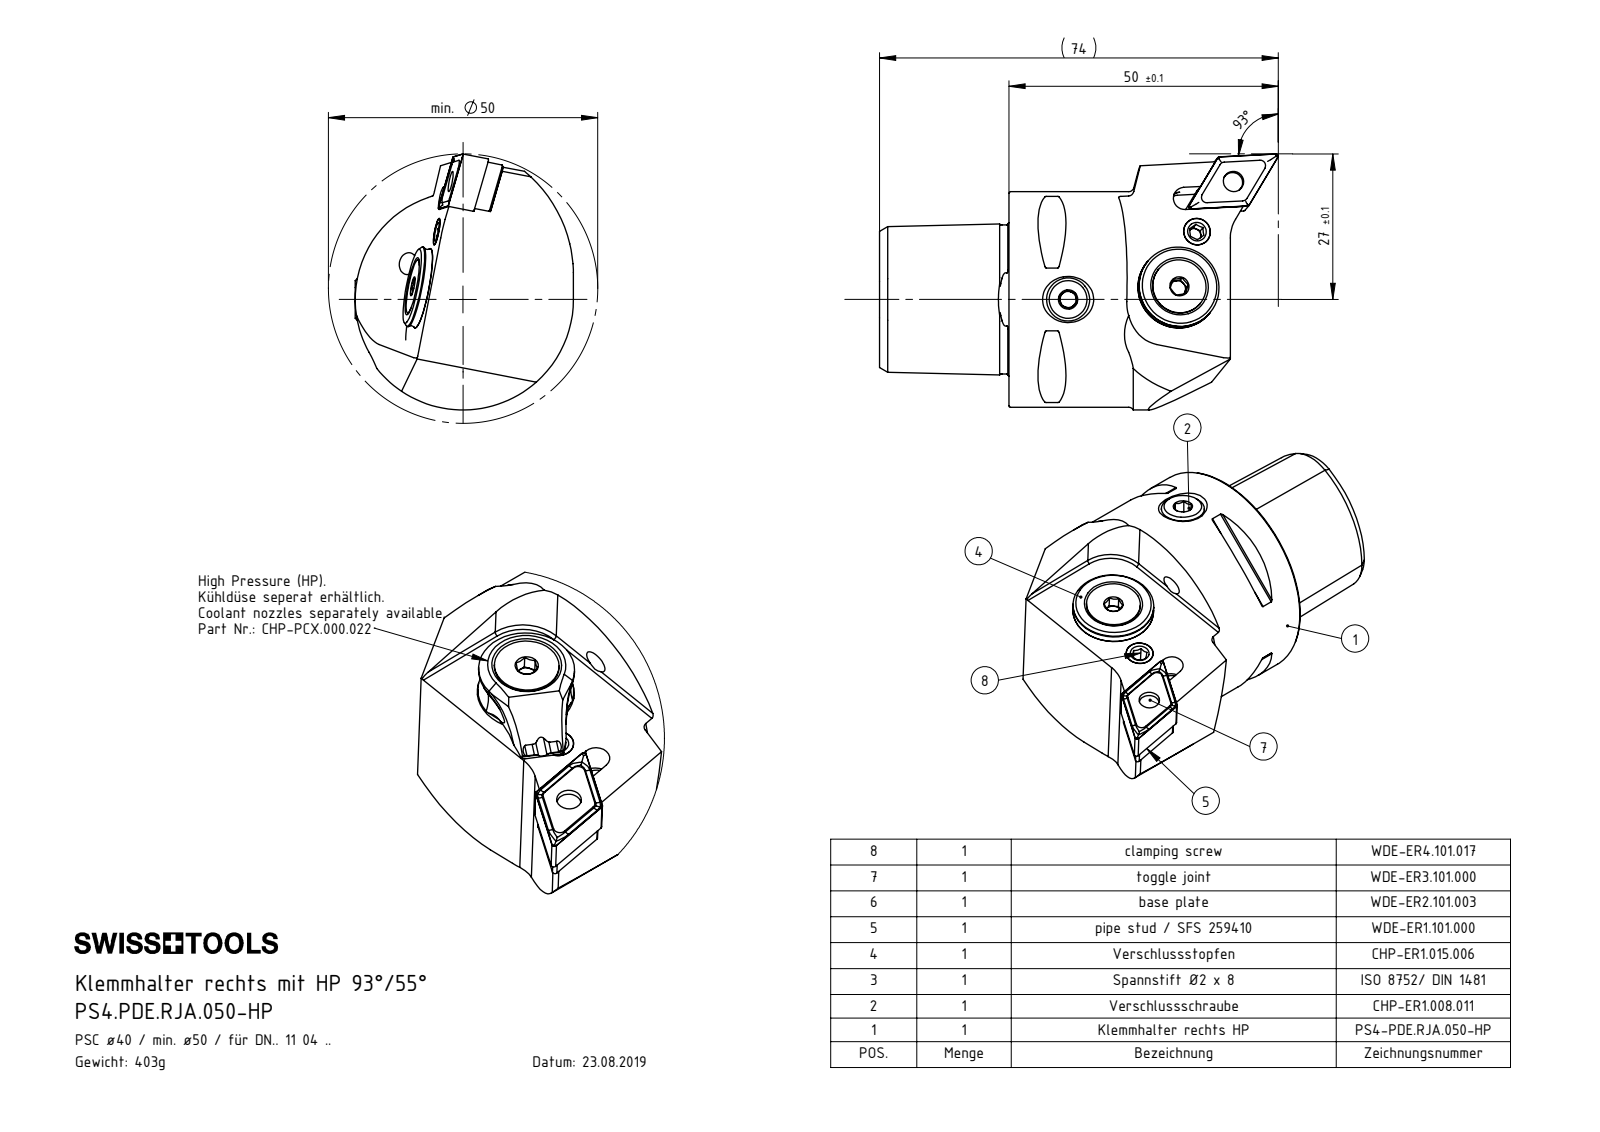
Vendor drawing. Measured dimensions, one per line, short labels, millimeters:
name: DIN 3771 - 6.5x1.5; CHP-ER1.008.011_A; DNMG110404; ISO 8752 2x8 (+8 more)
written by: SolidWorks 2022 (CONFIG_CONTROL_DESIGN)
unit: mm
bodies: 12 solids, 563 faces (159 planar, 143 cylindrical, 261 other)
size: 74 × 47.49 × 40.5
volume: 52 225 mm³; area: 17 398 mm²
holes: 2× ⌀3.3, 2× ⌀5, 1× ⌀1.2, 1× ⌀2, 1× ⌀2.5, 1× ⌀3, 1× ⌀3.81, 1× ⌀4, 1× ⌀4.2, 1× ⌀4.6, 1× ⌀4.8, 1× ⌀5.3
bosses: 1× ⌀40, 1× ⌀14.85, 1× ⌀13.4, 1× ⌀10, 1× ⌀8, 1× ⌀6, 1× ⌀5.9, 1× ⌀5.5
rounds: 9× R0.3, 7× R1, 4× R0.4, 4× R0.5, 4× R0.8, 4× R2.1, 3× R6, 2× R1.1
face distances: 4.5, 9, 24, 21.04, 4.61, 15.52, 1.5, 3, 0.83, 11.01
hole spacings: 11.4, 11.42, 22.94, 1, 4.5, 4.51, 4.52, 4.53
